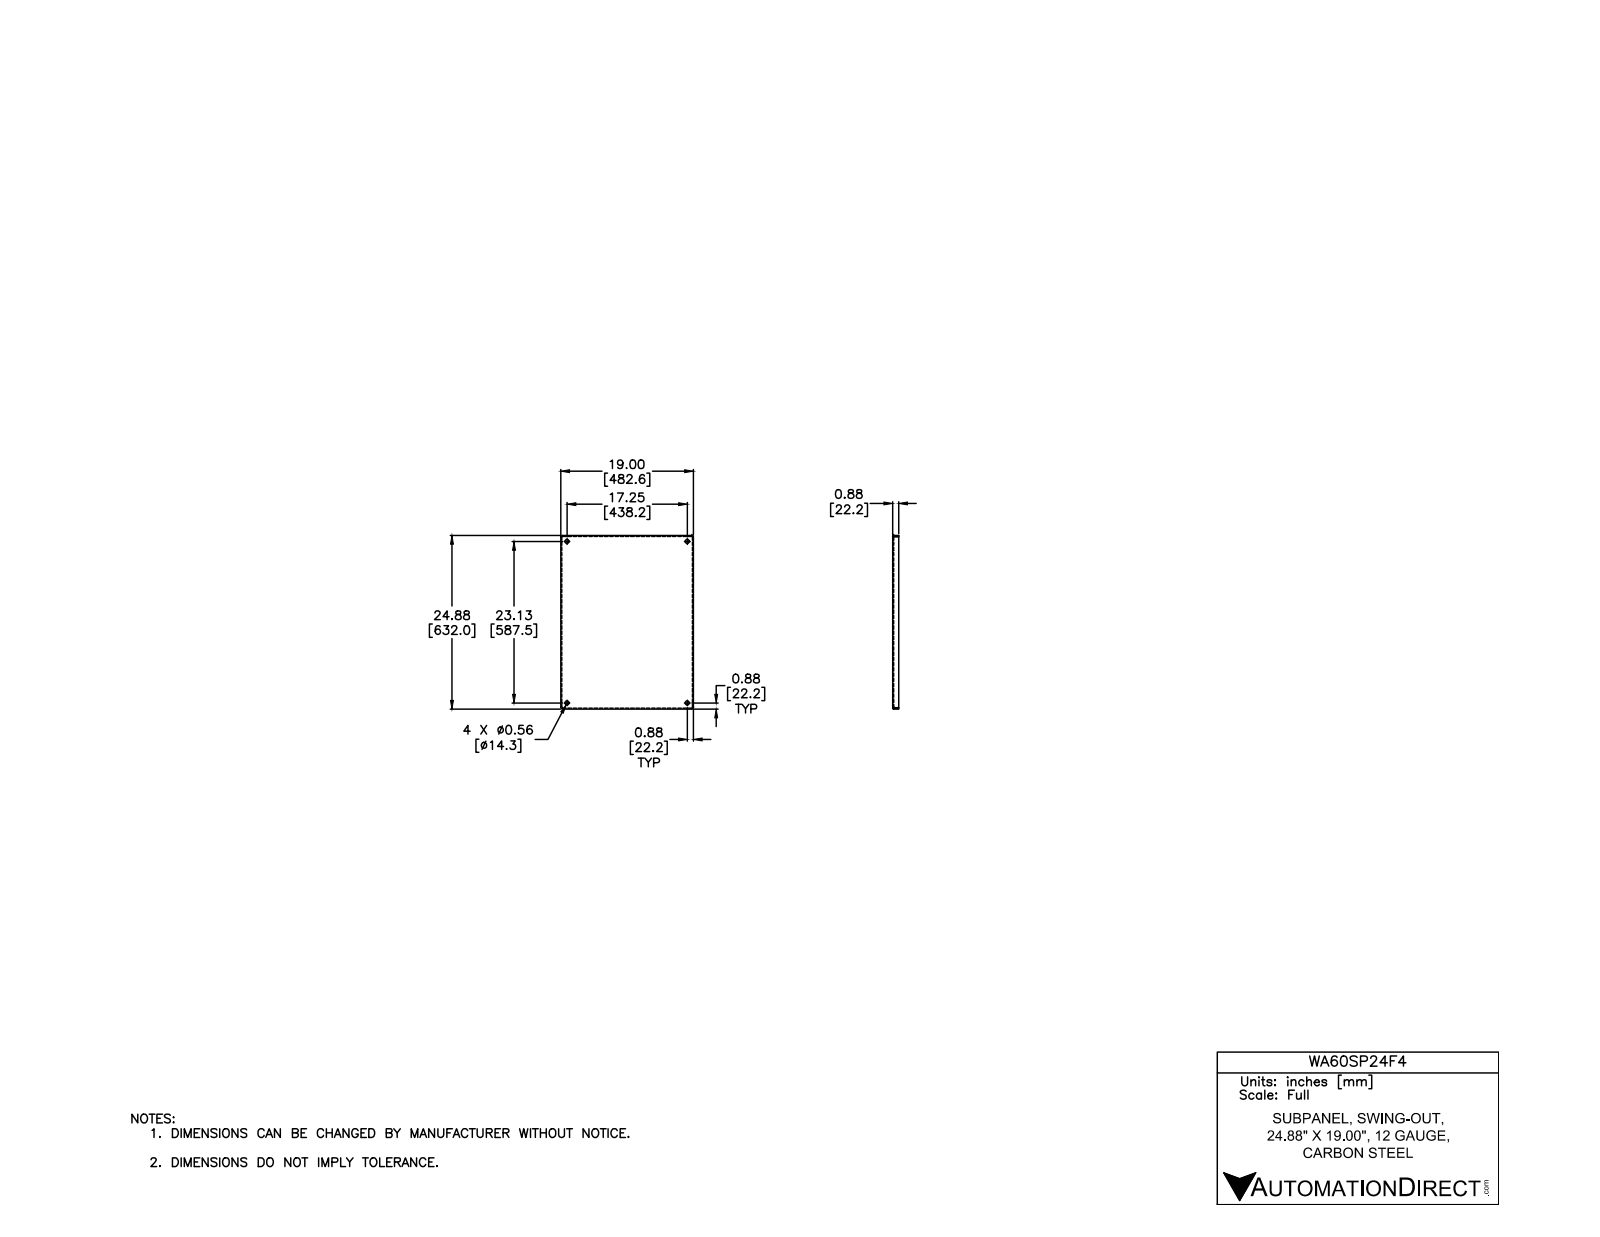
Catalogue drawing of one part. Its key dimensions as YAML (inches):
part_name: "WA60SP24F3-WA90SP36F4"
step_written_by: "Autodesk Inventor 2012 (AUTOMOTIVE_DESIGN)"
units: inches
bodies: {solids: 1, faces: 42, planar: 22, cylindrical: 12, other: 8}
overall_size: [24.88, 19, 0.875]
volume: 50.28
surface_area: 1082
round_holes:
  - {diameter: 0.563, count: 4}
partial_cylinders:
  - {radius: 0.031, count: 4}
  - {radius: 0.125, count: 4}
face_to_face_distances: [0.094, 18.906, 24.786, 19, 18.813, 24.693, 24.88, 0.781, 0.875, 0.16]
hole_center_spacings: [17.25, 23.13, 28.855]
